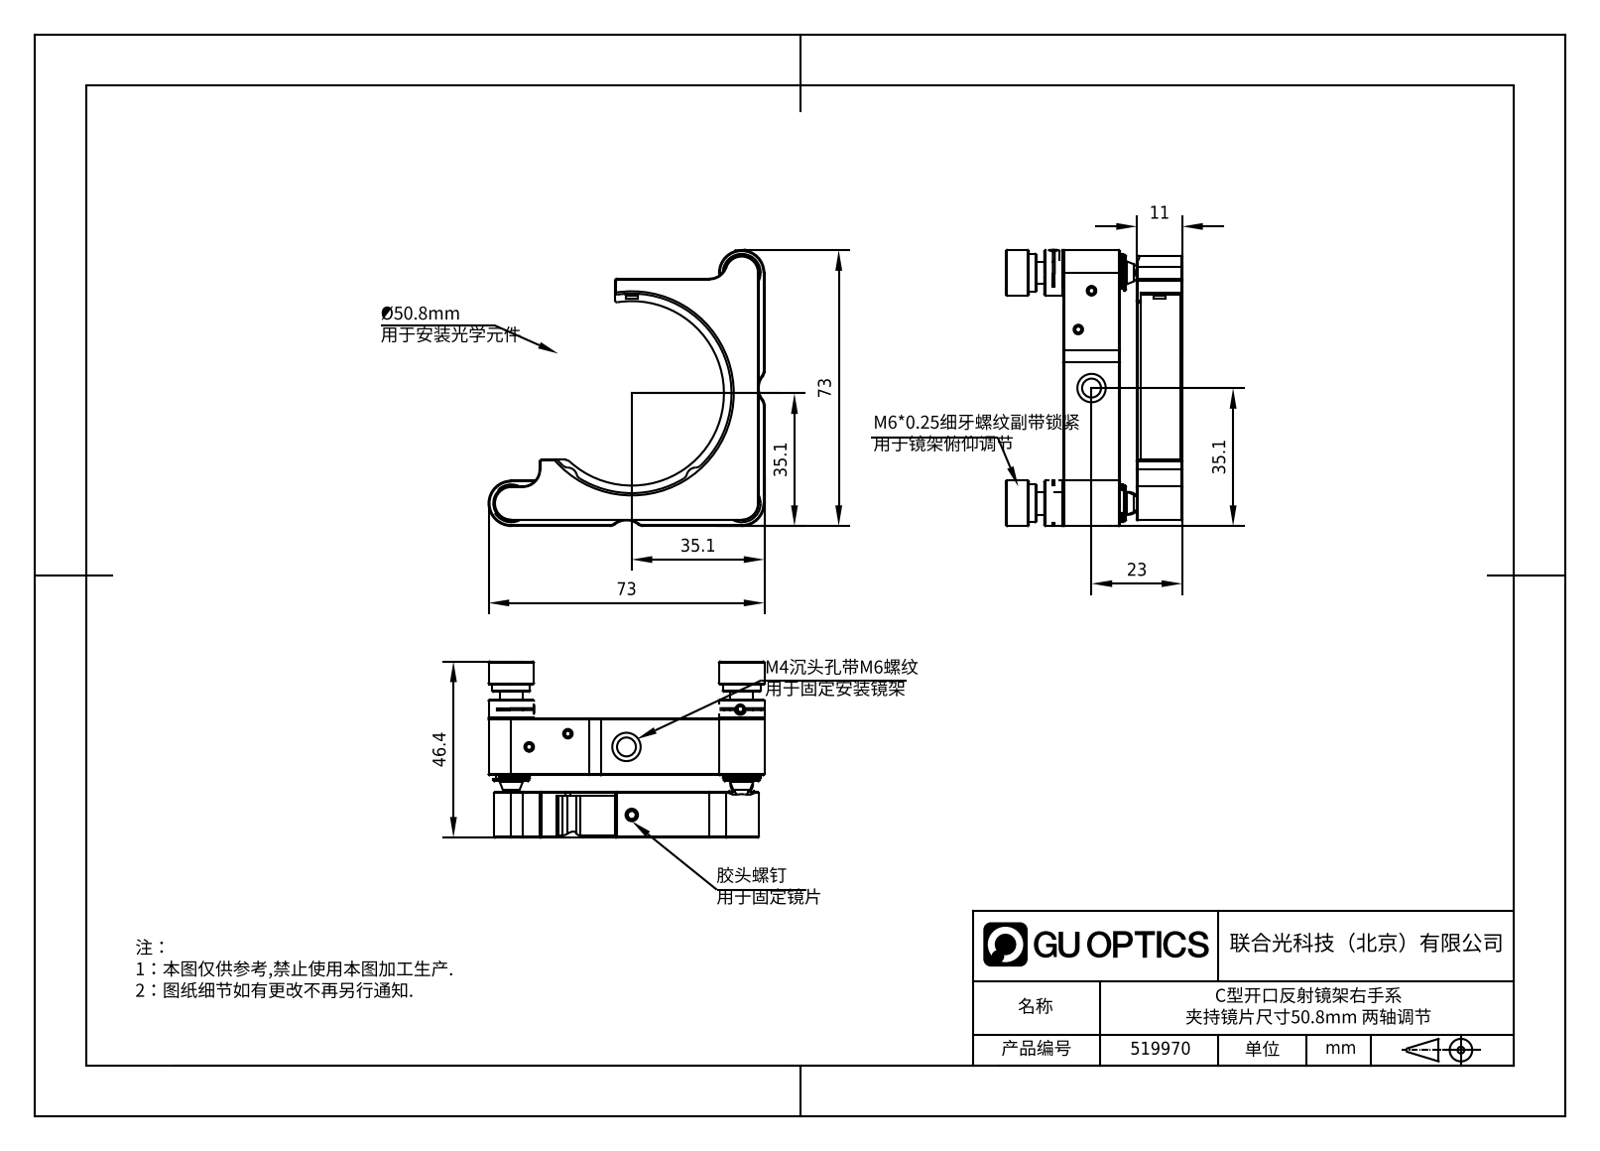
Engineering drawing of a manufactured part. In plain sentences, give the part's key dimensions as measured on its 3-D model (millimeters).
Its 3-D file was written by "SolidWorks 2021 (CONFIG_CONTROL_DESIGN)". It is 0 solids with 448 faces: 150 planar, 144 cylindrical and 154 other. Overall it measures 73.07 by 73 by 46.6 millimeters. Round holes: 10 of diameter 2.5, 4 of diameter 6, 3 of diameter 5, 2 of diameter 4, 2 of diameter 7.5, 1 of diameter 3.3, 1 of diameter 9.5. Round bosses or shafts: 6 of diameter 3, 3 of diameter 10, 2 of diameter 12, 2 of diameter 9.5, 2 of diameter 8, 2 of diameter 6, 2 of diameter 4. Partial cylindrical surfaces (rounded edges, fillets, slot ends): 9 of radius 2, 5 of radius 0.5, 5 of radius 4.5, 2 of radius 0.2, 2 of radius 2.5, 2 of radius 5, 2 of radius 10, 1 of radius 6. The main face-to-face distances are 12, 1.5, 4.5, 31.5, 19.5, 15, 16.5, 10.5, 1, 11. The hole center spacings are 31, 15, 25.3, 46, 10.83, 15.89, 22.47, 23.5.
